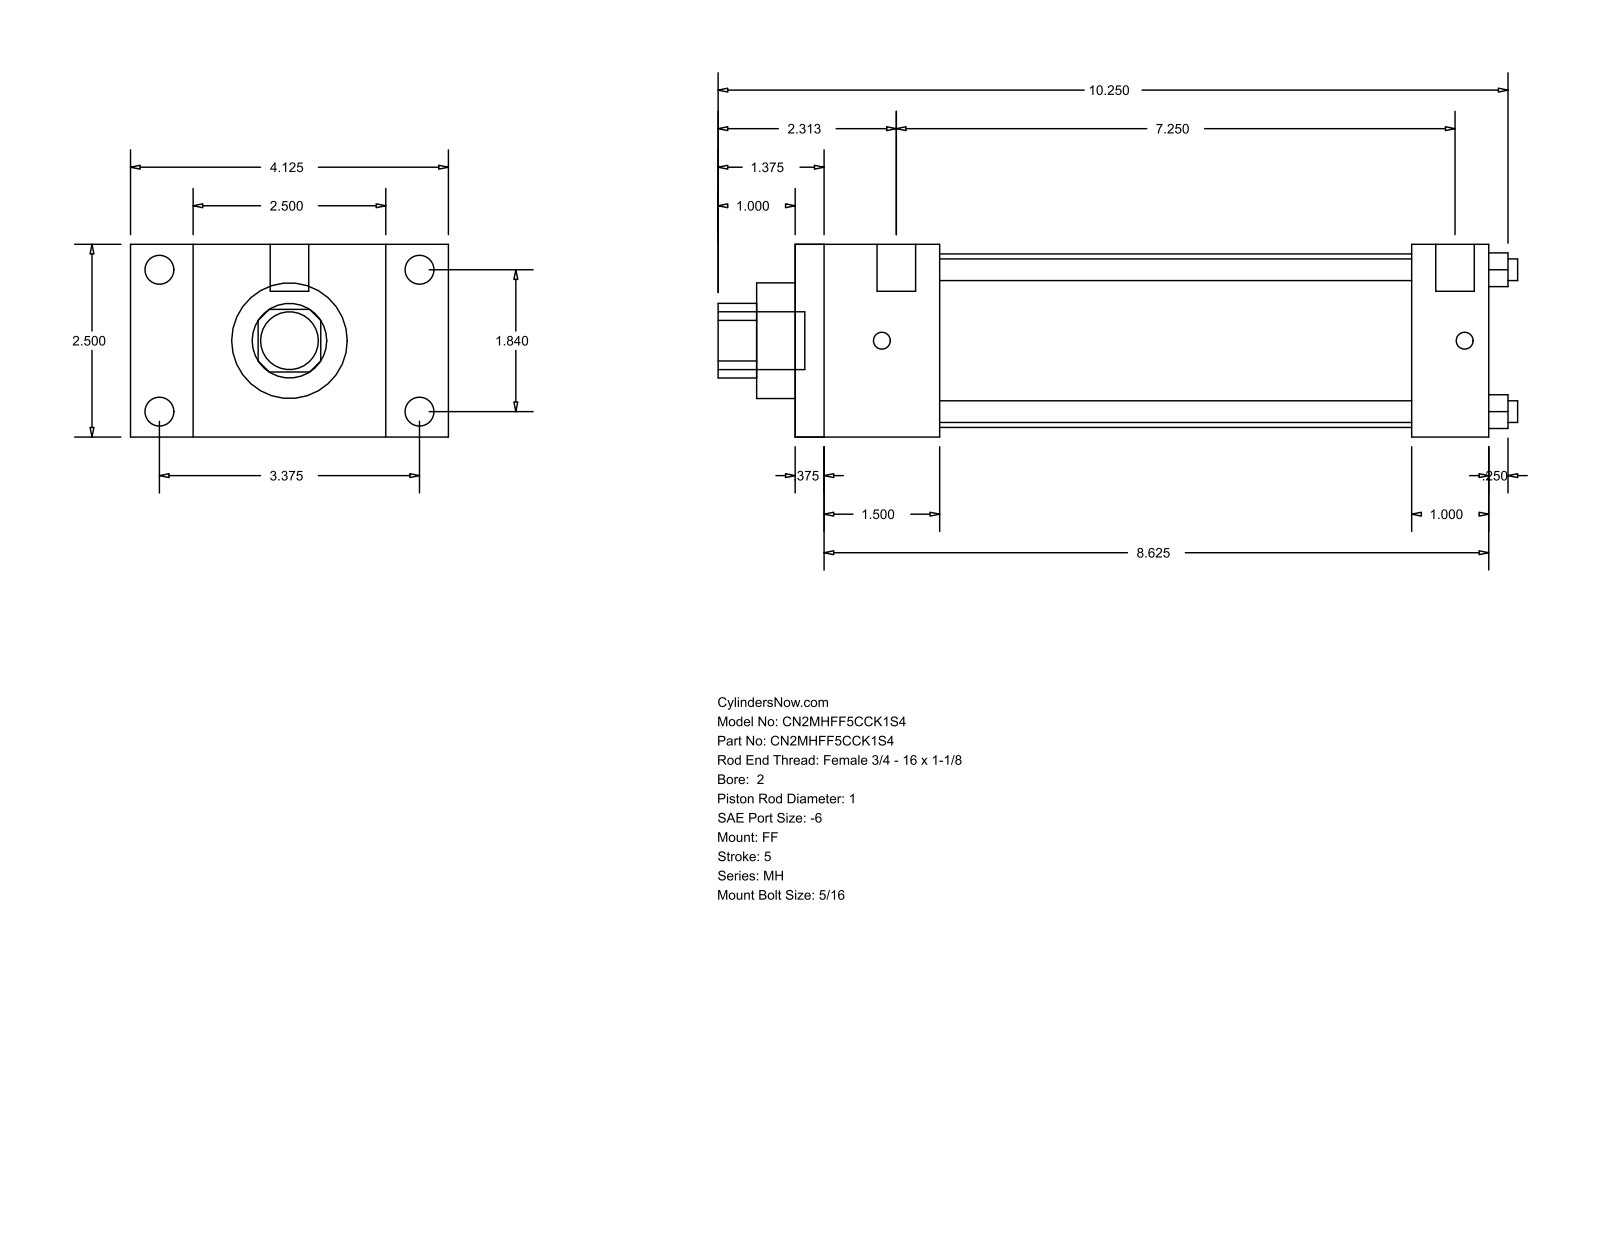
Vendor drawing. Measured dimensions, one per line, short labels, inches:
name: MH_FF__0200_1
written by: GSSL Pune (CONFIG_CONTROL_DESIGN)
unit: in
bodies: 0 solids, 92 faces (64 planar, 28 cylindrical, 0 other)
size: 10.375 × 4.125 × 2.5
holes: 4× ⌀0.281, 1× ⌀1, 1× ⌀1.5, 1× ⌀2.25
bosses: 4× ⌀0.375, 4× ⌀0.219, 2× ⌀0.5, 1× ⌀0.75
rounds: 1× R0.484
face distances: 2.5, 9, 0.375, 8.625, 0.813, 1, 1.875, 8, 1.5, 7.625
hole spacings: 1.301, 1.84, 2.602
